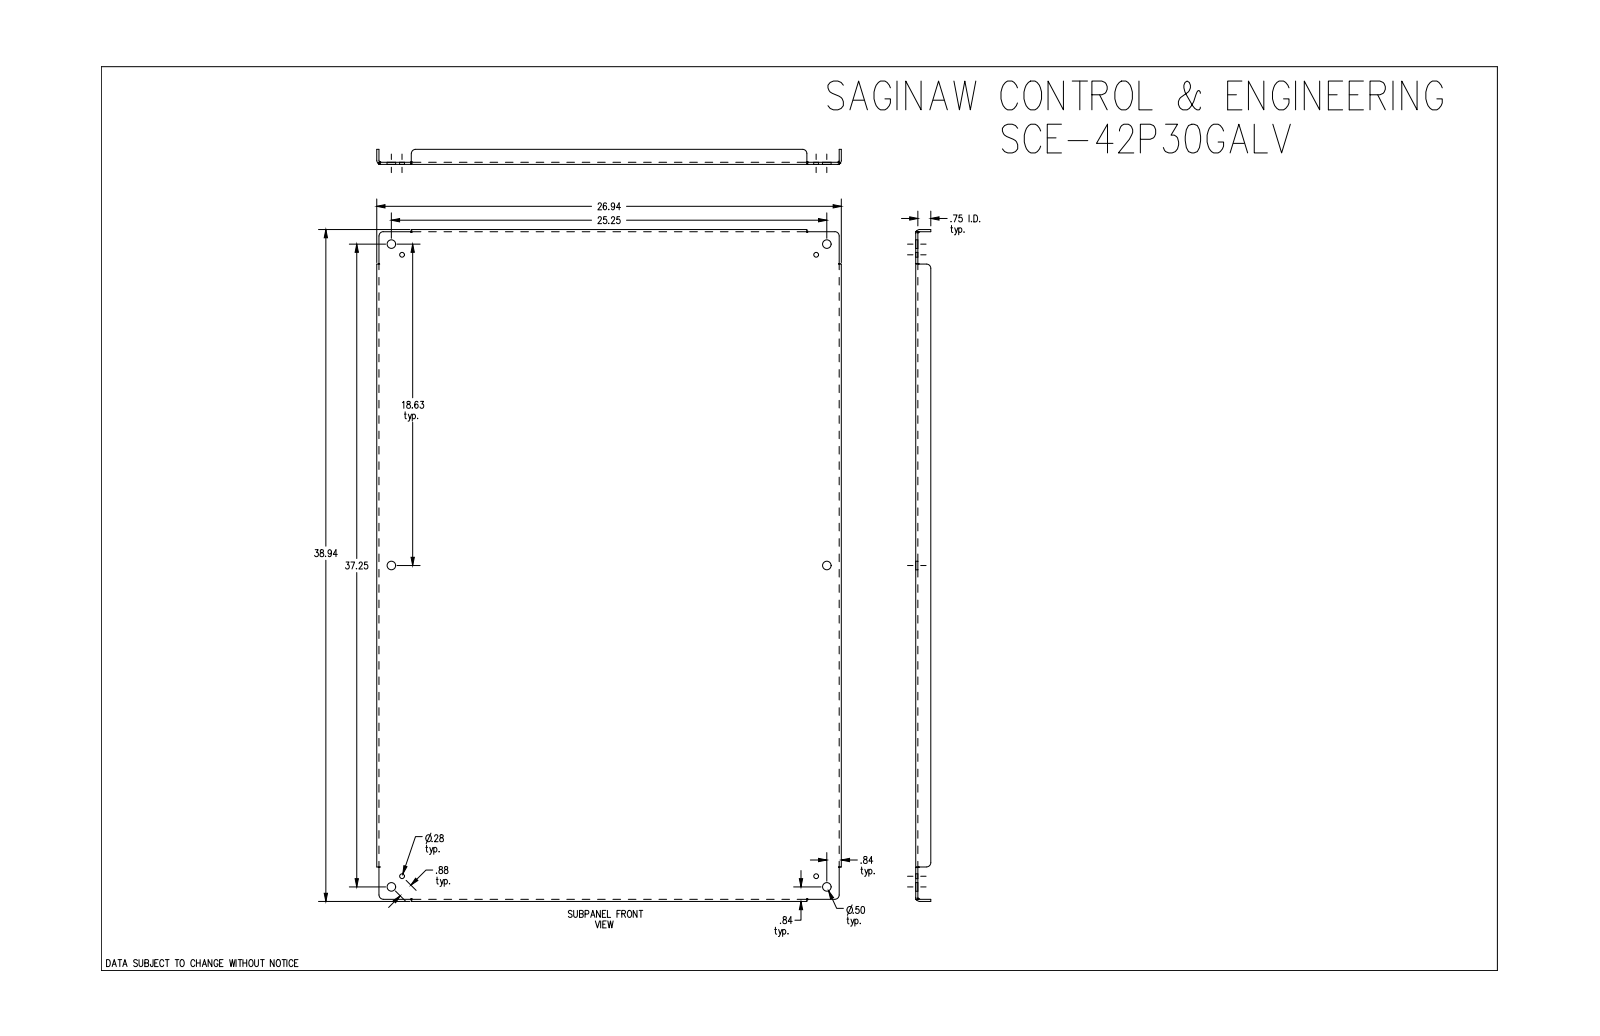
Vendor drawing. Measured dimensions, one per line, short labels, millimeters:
name: SCE-42P30GALV
written by: SolidWorks 2019 (CONFIG_CONTROL_DESIGN)
unit: mm
bodies: 1 solid, 84 faces (30 planar, 30 cylindrical, 24 other)
size: 989 × 684.2 × 22.2
volume: 2 301 000 mm³; area: 1 462 000 mm²
holes: 6× ⌀12.7, 4× ⌀7.1
rounds: 8× R6.4, 4× R2.8, 4× R6
face distances: 3.2, 3.2, 681.1, 985.9, 677.8, 684.2, 982.6, 989, 19.1, 22.2
hole spacings: 22.2, 457.6, 473.1, 625.8, 775, 797, 930.6, 1121.2
